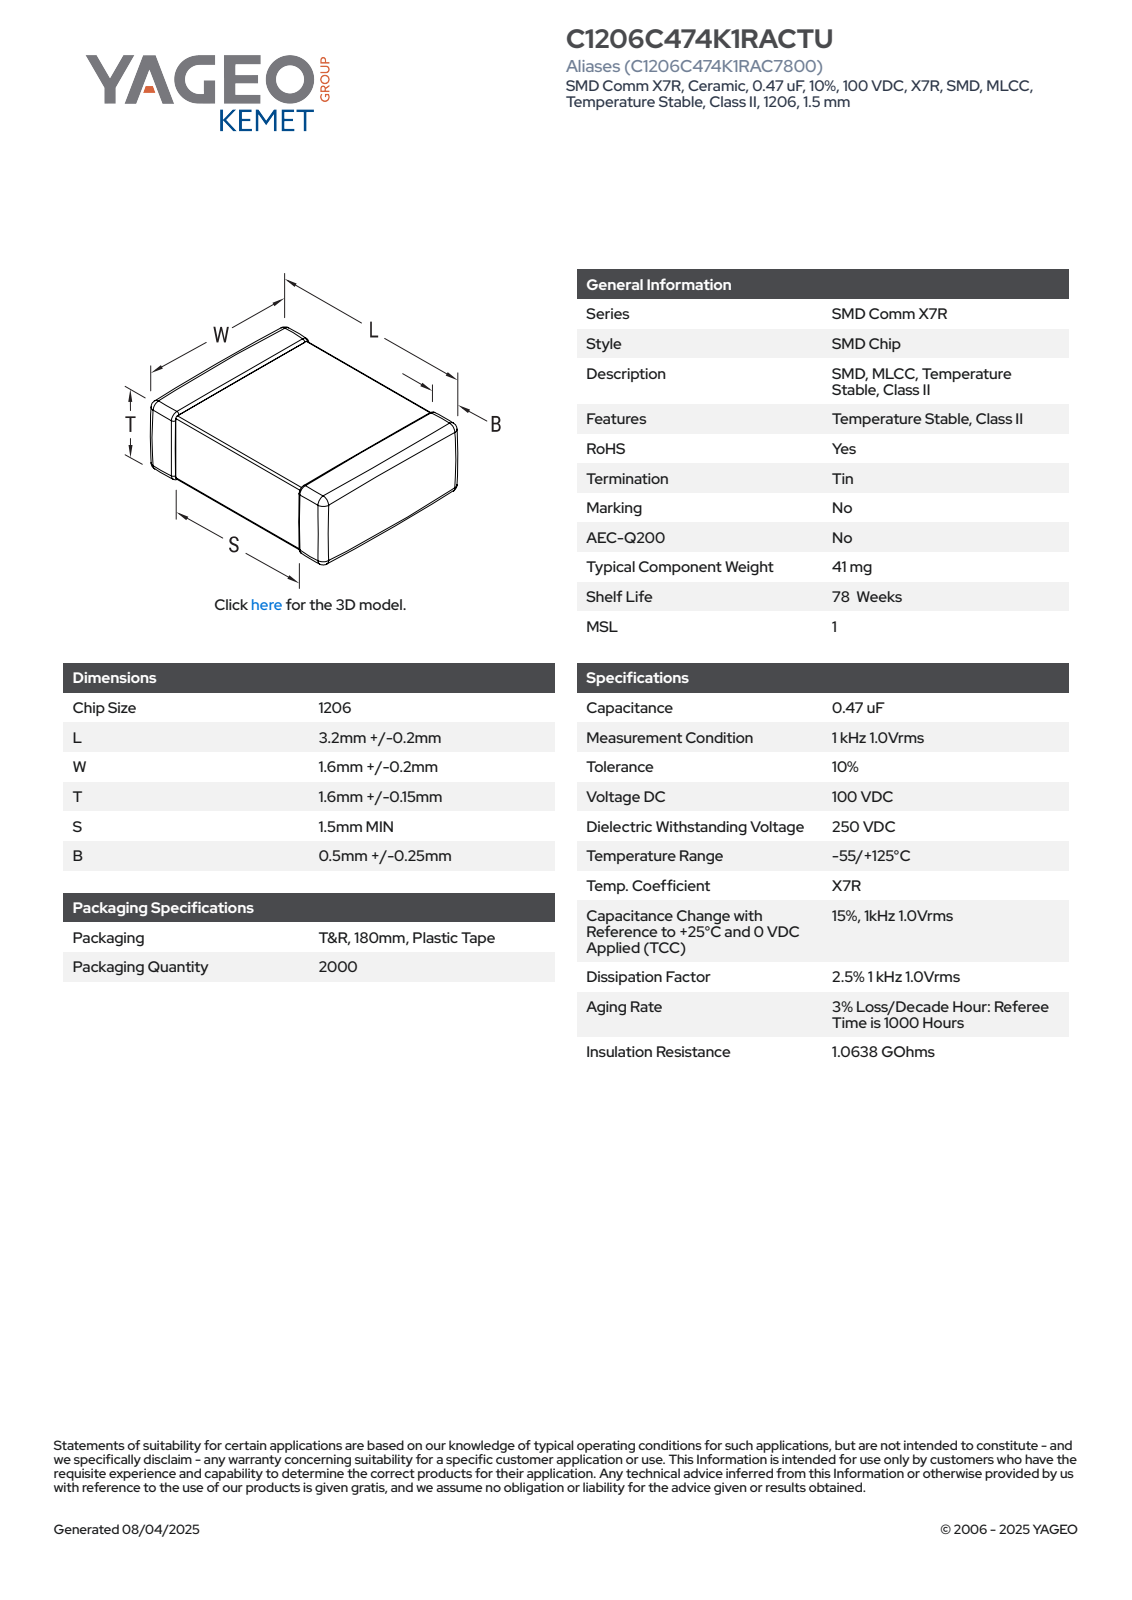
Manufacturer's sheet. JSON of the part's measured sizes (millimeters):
{"part_name": "CCS_CCSTDNOS_1206_L3.4W1.8T1.75B0.75", "step_written_by": "SolidWorks 2014 (AUTOMOTIVE_DESIGN)", "units": "millimeters", "bodies": {"solids": 4, "faces": 125, "planar": 71, "cylindrical": 38, "other": 16}, "overall_size": [3.4, 1.8, 1.75], "volume_mm3": 10, "surface_area_mm2": 30, "face_to_face_distances": [1.71, 1.76, 1.72, 1.67, 3.4, 1.75, 1.8, 1.68, 0.99, 0.75]}
